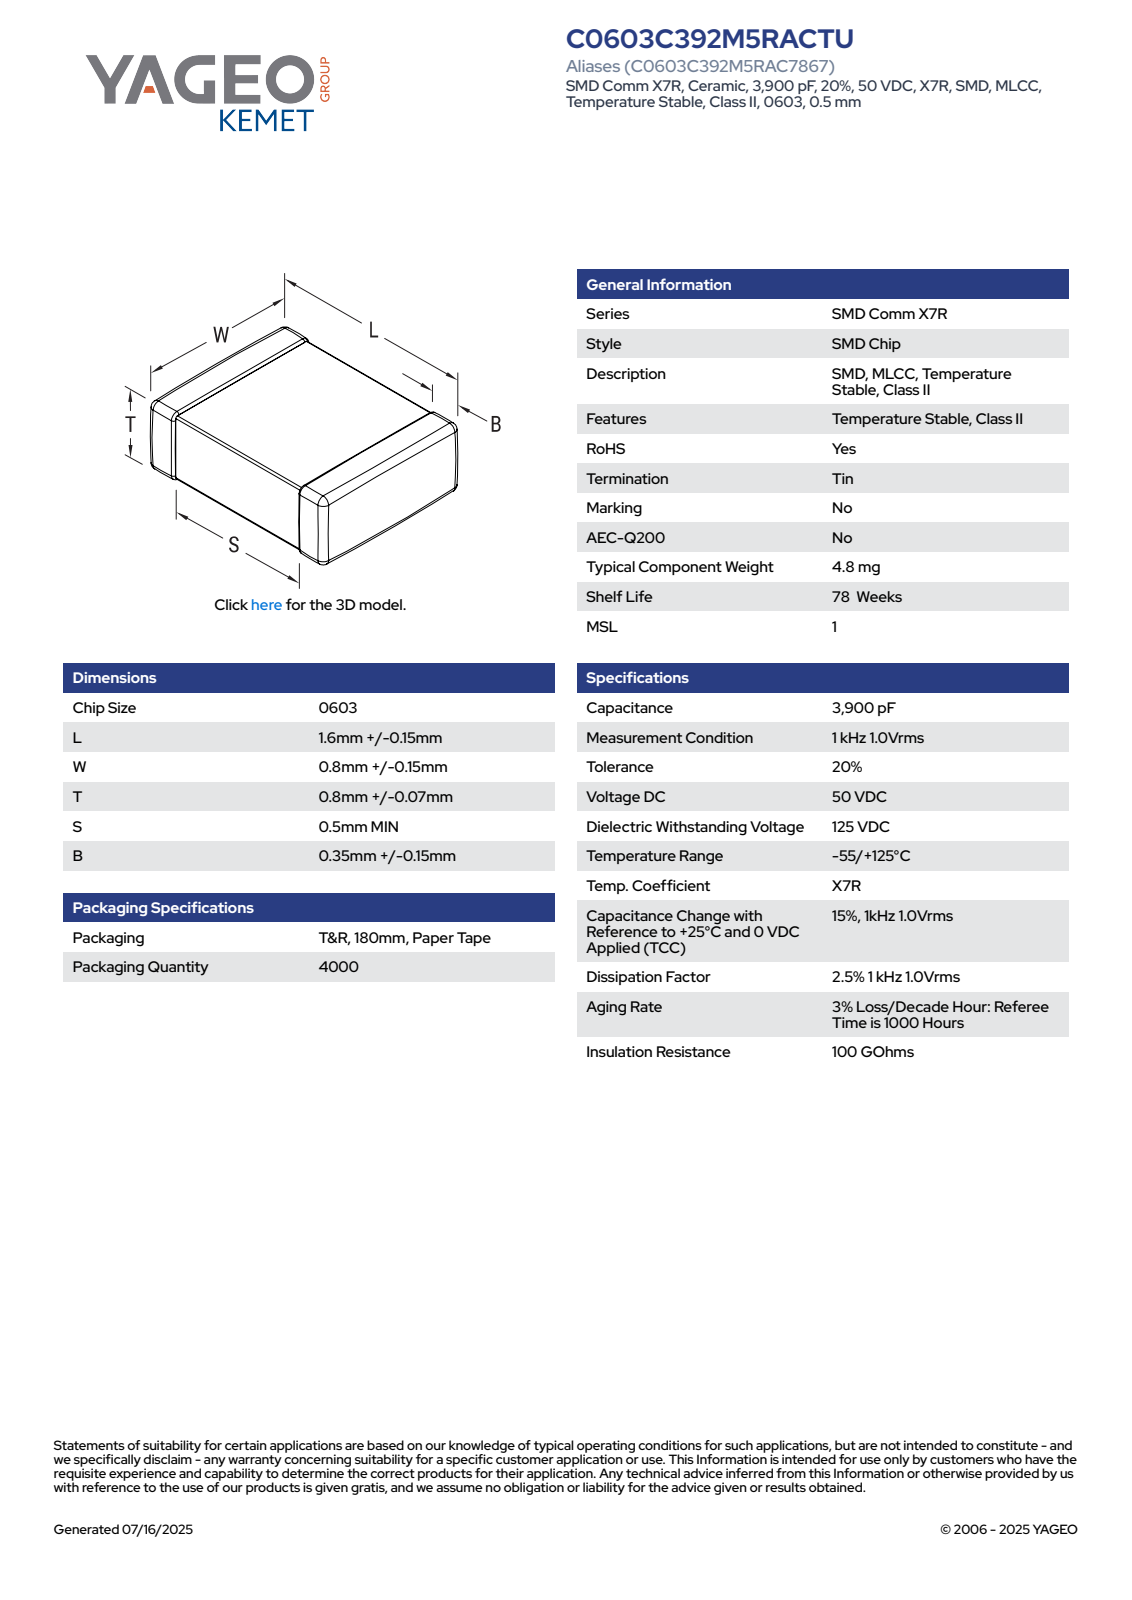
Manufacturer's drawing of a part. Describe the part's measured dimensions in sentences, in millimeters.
The part is named "CCS_CCSTD_0603_L1.75W0.95T0.87B0.35". Its 3-D file was written by "SolidWorks 2021 (AUTOMOTIVE_DESIGN)". It is 4 solids with 125 faces: 71 planar, 38 cylindrical and 16 other. Overall it measures 1.75 by 0.95 by 0.87 millimeters. Its volume is 1 cubic millimeters and its surface area 8 square millimeters. The main face-to-face distances are 0.85, 0.93, 0.87, 0.95, 1.75, 0.83, 0.91, 0.86, 0.84, 0.81.
